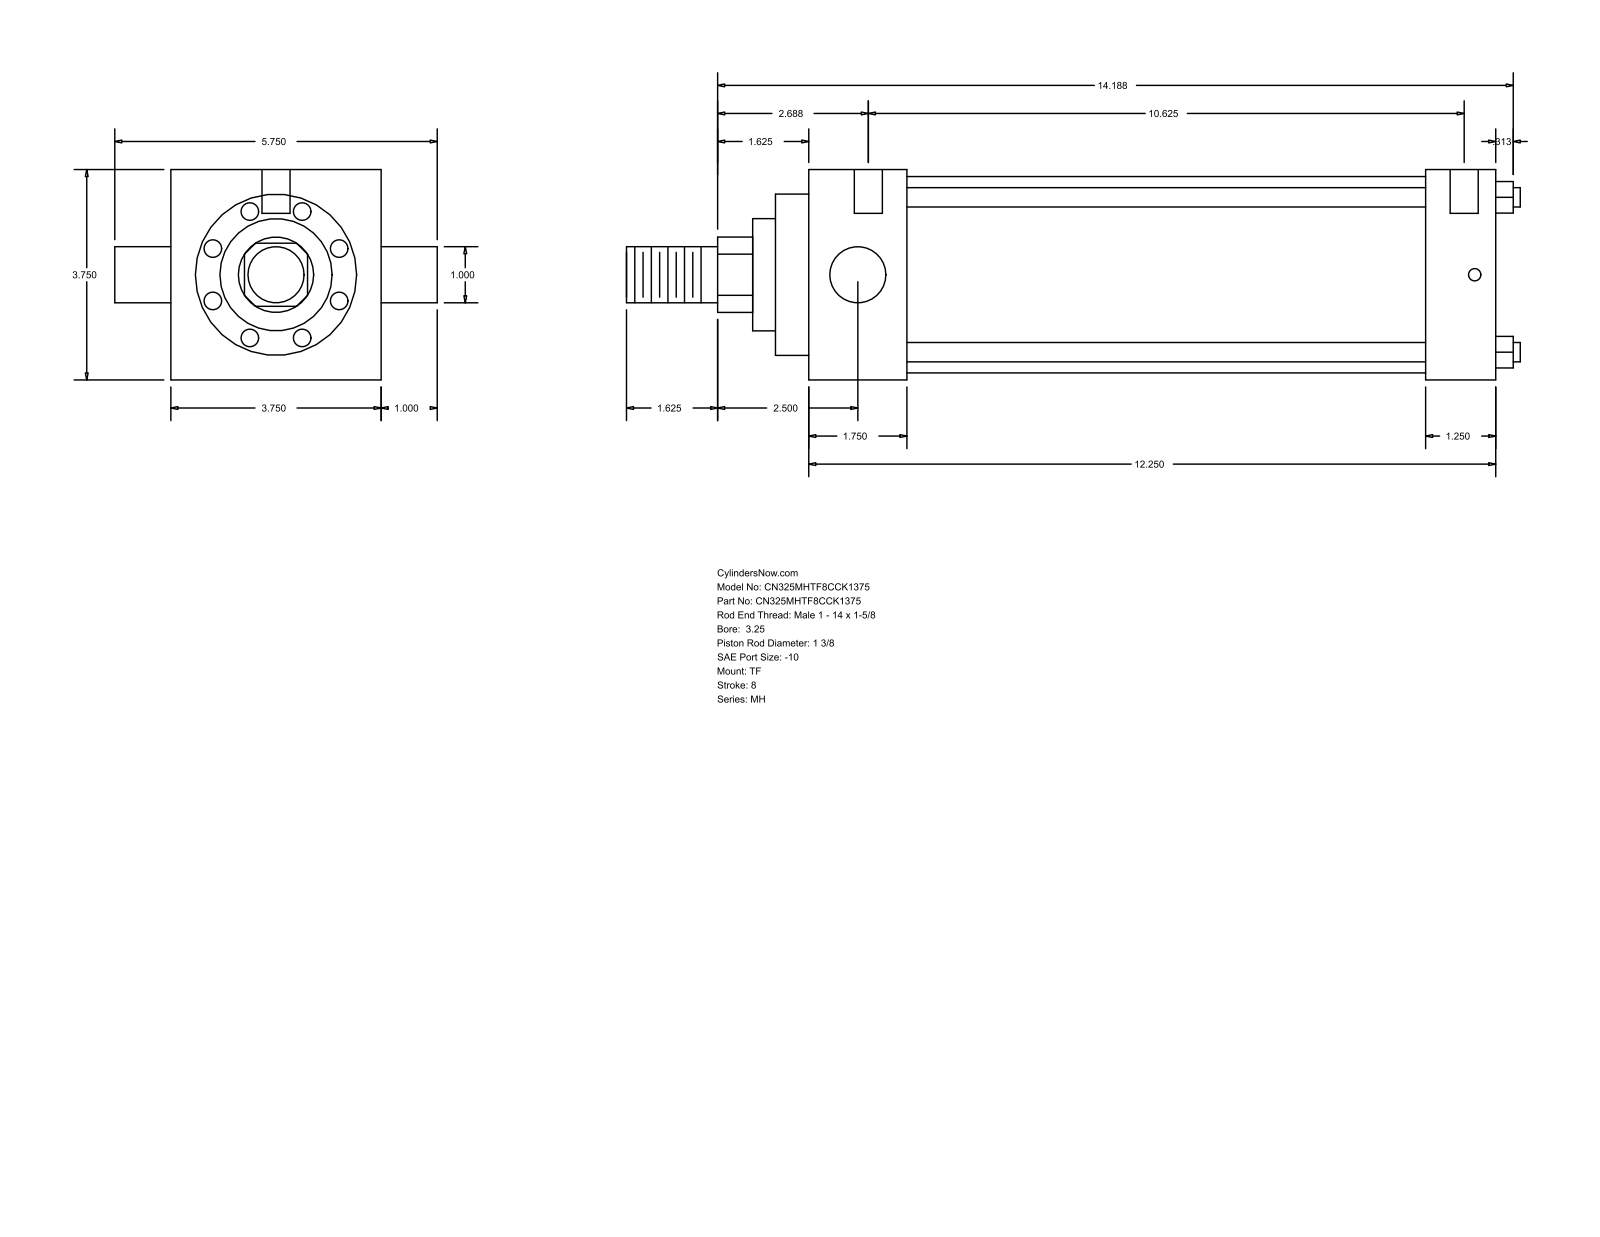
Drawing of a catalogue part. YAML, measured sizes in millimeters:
part_name: "MH_TF__0325_1.375"
step_written_by: "GSSL Pune (CONFIG_CONTROL_DESIGN)"
units: millimeters
bodies: {solids: 0, faces: 86, planar: 61, cylindrical: 25, other: 0}
overall_size: [404.81, 146.05, 95.25]
round_holes:
  - {diameter: 5.56, count: 3}
  - {diameter: 12.7, count: 2}
round_bosses_or_shafts:
  - {diameter: 8.76, count: 4}
  - {diameter: 25.4, count: 2}
  - {diameter: 88.9, count: 1}
  - {diameter: 73.03, count: 1}
  - {diameter: 50.8, count: 1}
  - {diameter: 34.92, count: 1}
partial_cylinders:
  - {radius: 17.06, count: 1}
face_to_face_distances: [95.24, 311.16, 44.45, 279.41, 234.96, 266.71, 31.75, 15.08, 59.53, 294.49]
hole_center_spacings: [1.59, 4.76, 269.88, 271.47, 274.64, 276.23]
